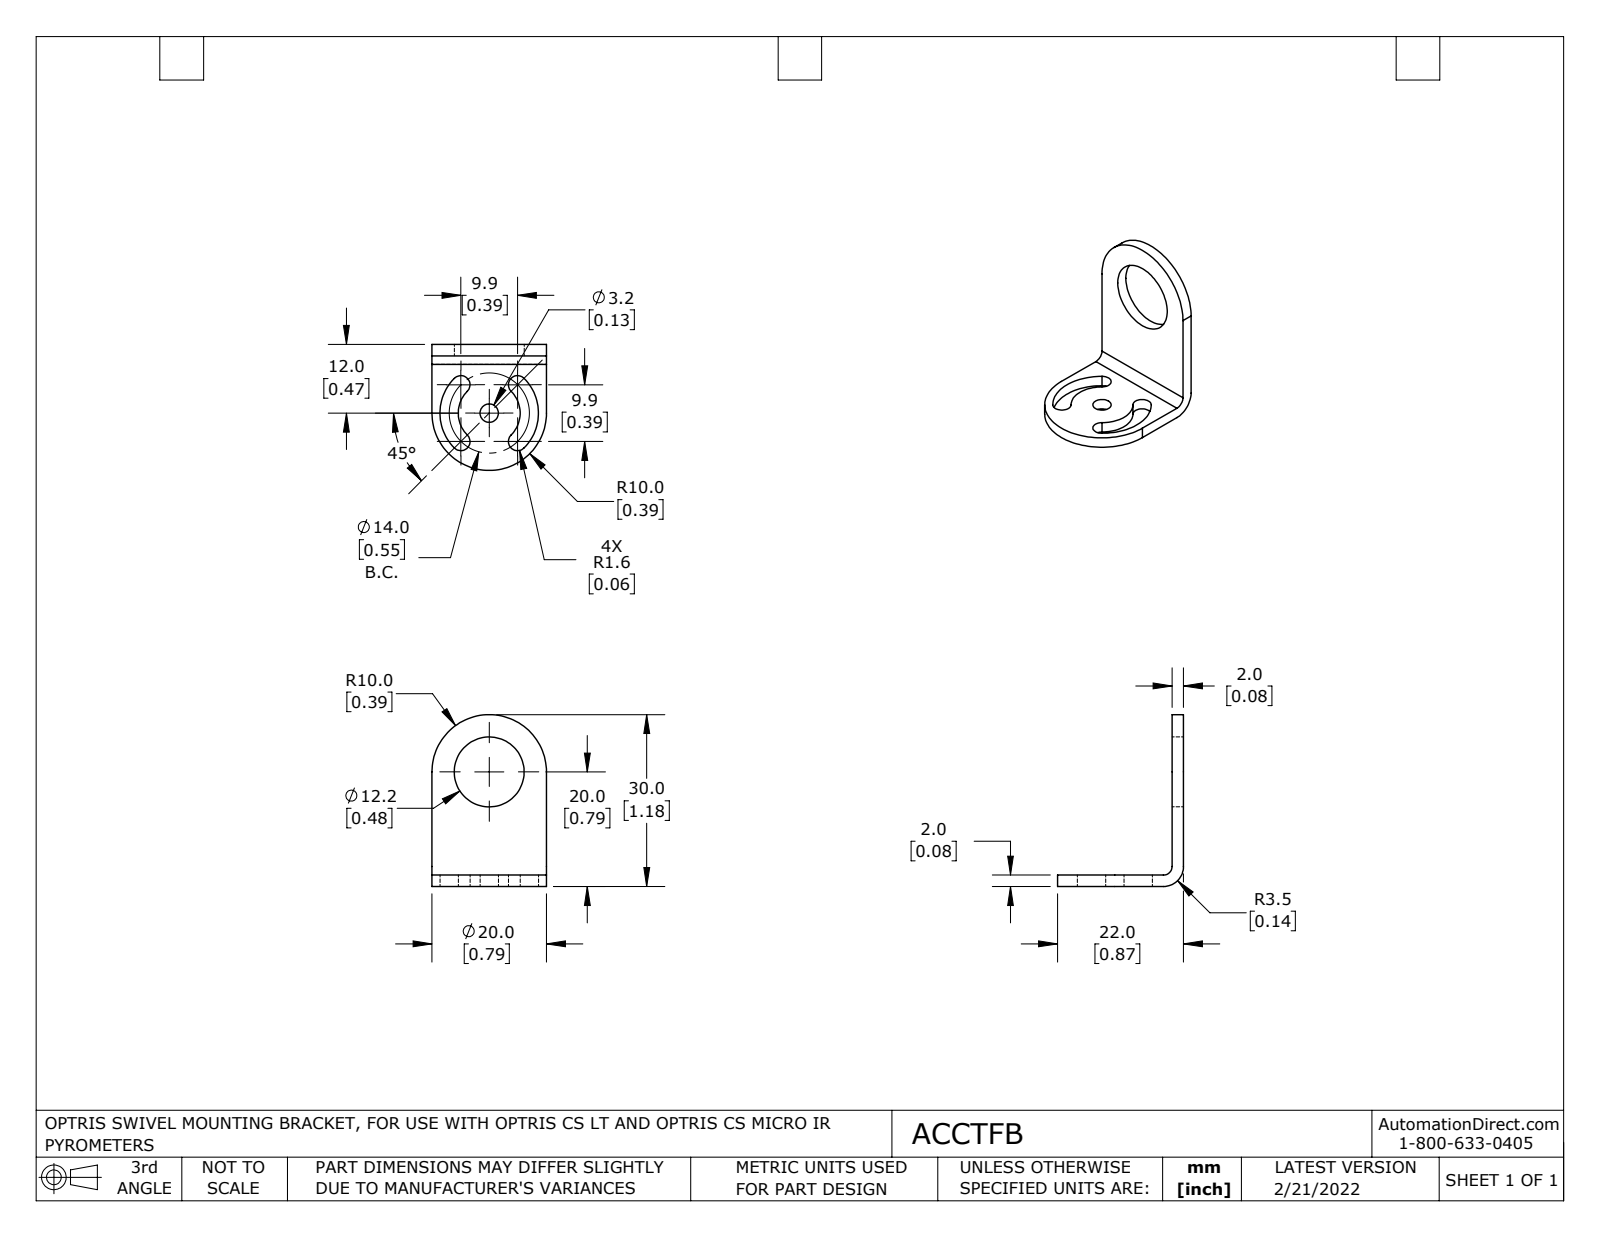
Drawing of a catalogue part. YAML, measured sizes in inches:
part_name: "ACCTFB - Mounting bracket, adjustable in one axis nc Coord"
step_written_by: "SolidWorks 2021 (AUTOMOTIVE_DESIGN)"
units: inches
bodies: {solids: 1, faces: 25, planar: 6, cylindrical: 19, other: 0}
overall_size: [1.181, 0.866, 0.787]
volume: 0.083
surface_area: 2.835
round_holes:
  - {diameter: 0.126, count: 1}
  - {diameter: 0.48, count: 1}
partial_cylinders:
  - {radius: 0.063, count: 4}
  - {radius: 0.394, count: 2}
  - {radius: 0.059, count: 1}
  - {radius: 0.138, count: 1}
  - {radius: 0.213, count: 1}
  - {radius: 0.339, count: 1}
face_to_face_distances: [0.079, 0.787]
